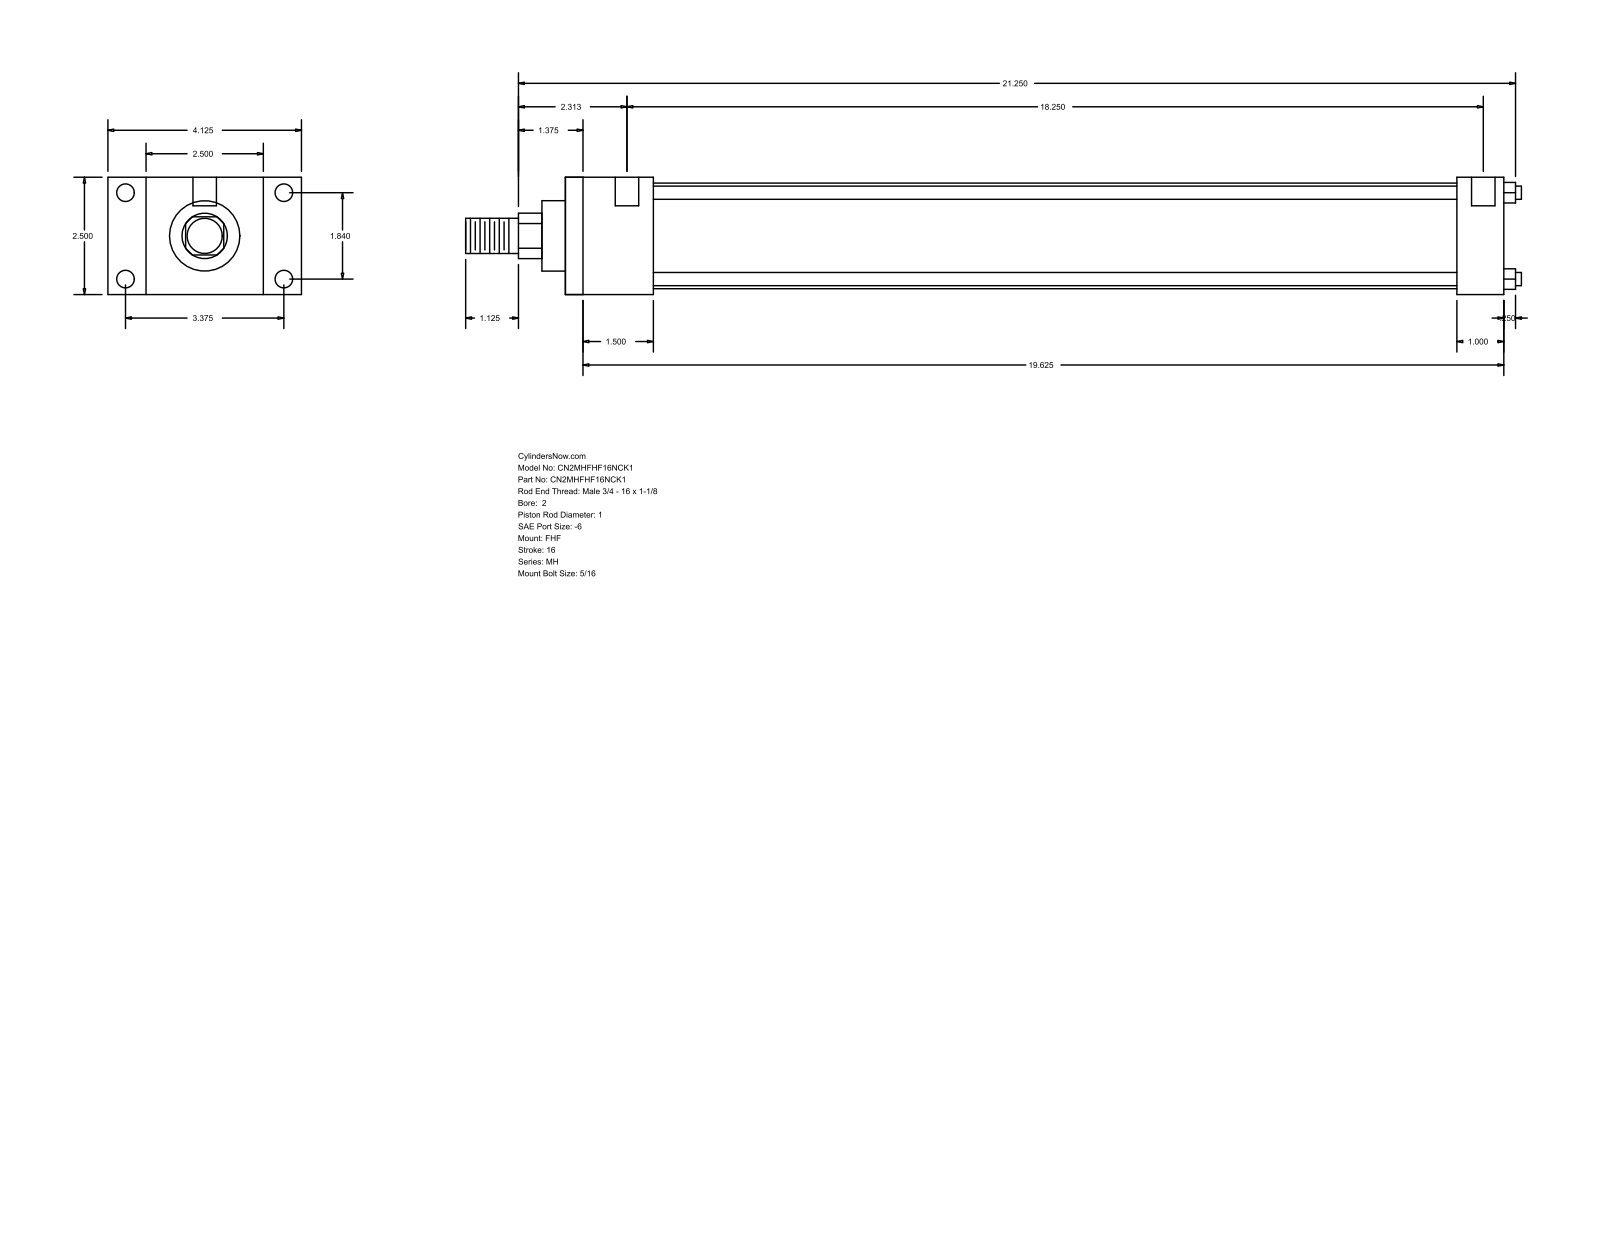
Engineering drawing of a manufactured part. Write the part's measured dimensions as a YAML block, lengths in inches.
part_name: "MH_FHF__0200_1"
step_written_by: "GSSL Pune (CONFIG_CONTROL_DESIGN)"
units: inches
bodies: {solids: 0, faces: 88, planar: 60, cylindrical: 28, other: 0}
overall_size: [22.5, 4.125, 2.5]
round_holes:
  - {diameter: 0.219, count: 4}
  - {diameter: 0.375, count: 4}
  - {diameter: 0.5, count: 2}
round_bosses_or_shafts:
  - {diameter: 0.281, count: 4}
  - {diameter: 2.25, count: 1}
  - {diameter: 1.5, count: 1}
  - {diameter: 1, count: 1}
  - {diameter: 0.75, count: 1}
partial_cylinders:
  - {radius: 0.484, count: 1}
face_to_face_distances: [2.5, 20, 1.875, 18.125, 0.813, 3.313, 4.125, 1, 19, 17.125]
hole_center_spacings: [1.84, 3.375, 3.844, 18.562, 0.125, 0.187, 18.25, 18.375]
